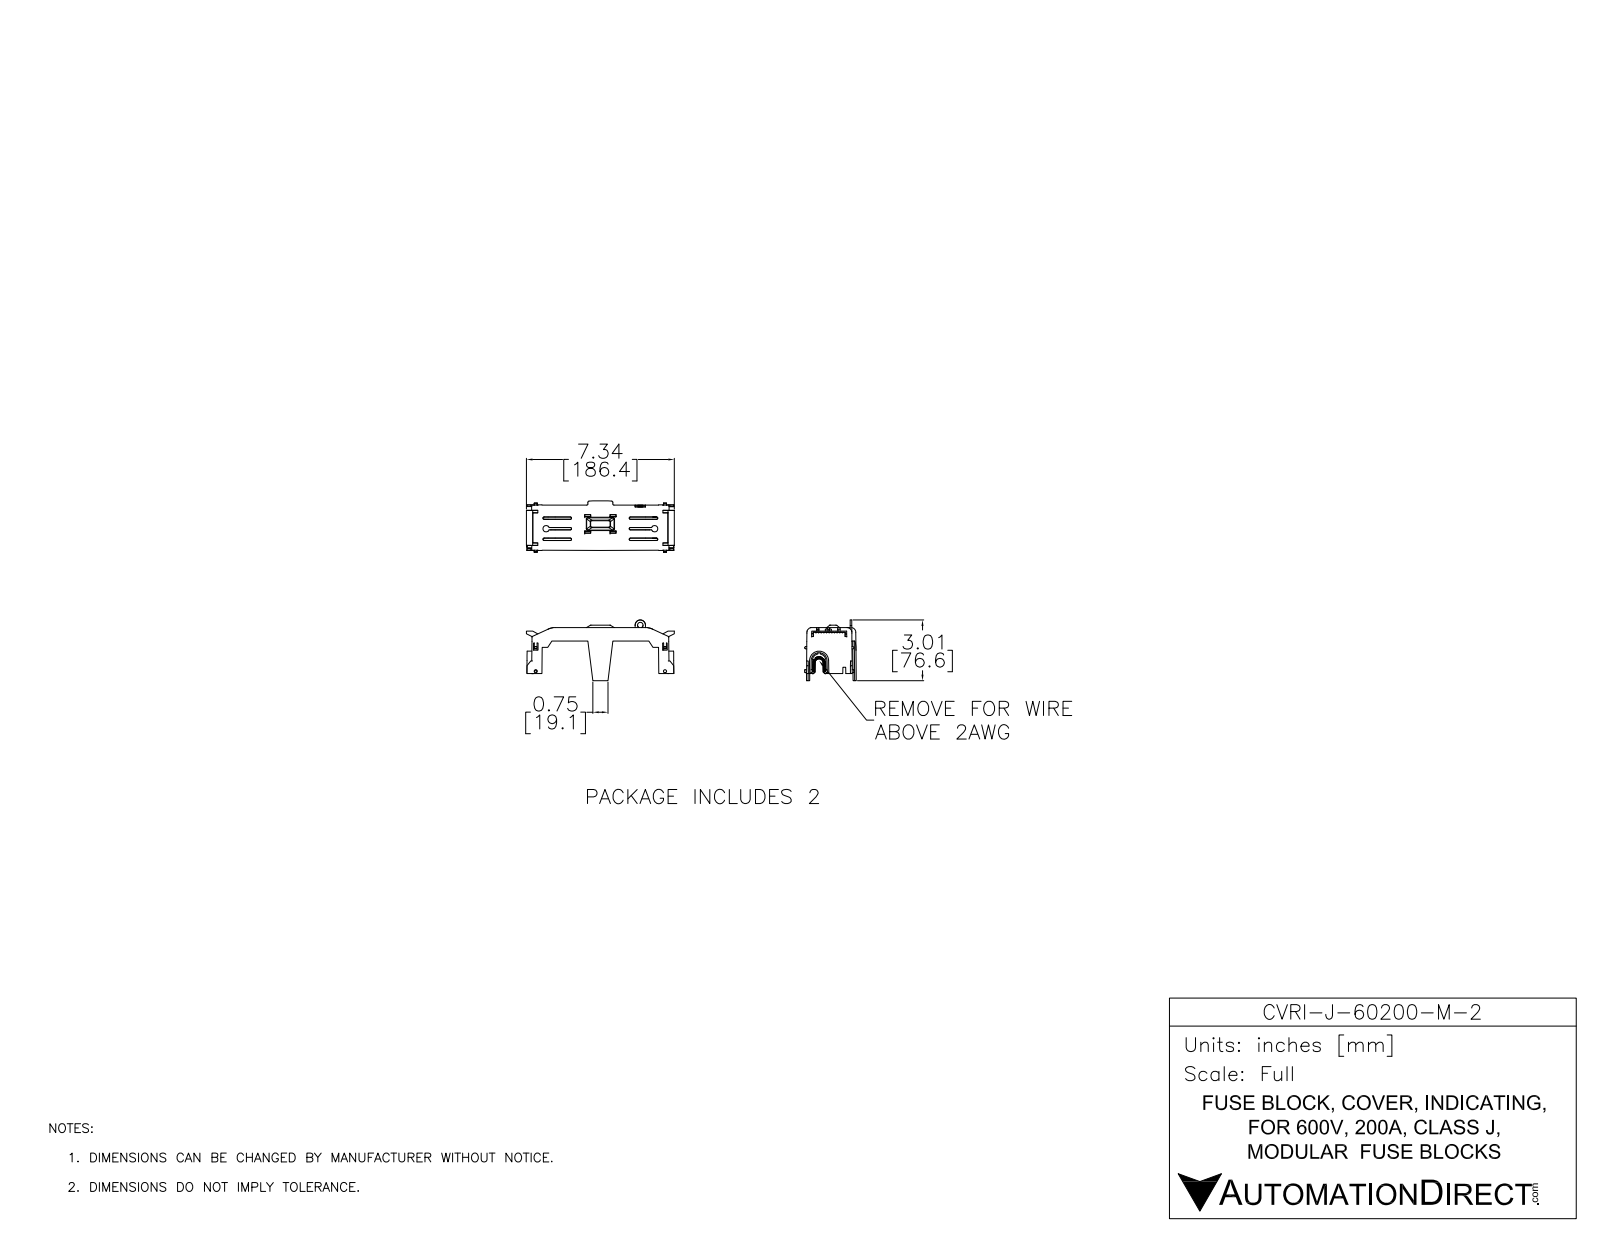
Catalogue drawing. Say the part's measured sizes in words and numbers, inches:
The part is named "CVRI-J-60200-M-2". Its 3-D file was written by "SolidWorks 2017 (AUTOMOTIVE_DESIGN)". It is 1 solid with 1408 faces: 920 planar, 113 cylindrical and 375 other. Overall it measures 7.34 by 3.014 by 2.553 inches. Its volume is 3.494 cubic inches and its surface area 95.88 square inches. Round holes: 1 of diameter 0.276. Partial cylindrical surfaces (rounded edges, fillets, slot ends): 12 of radius 0.039, 9 of radius 0.236, 8 of radius 0.118, 7 of radius 0.157, 6 of radius 0.035, 4 of radius 0.059, 2 of radius 0.01, 2 of radius 0.02. The main face-to-face distances are 0.079, 0.197, 0.118, 0.276, 0.512, 0.606, 0.095, 0.174, 0.803, 0.256.
